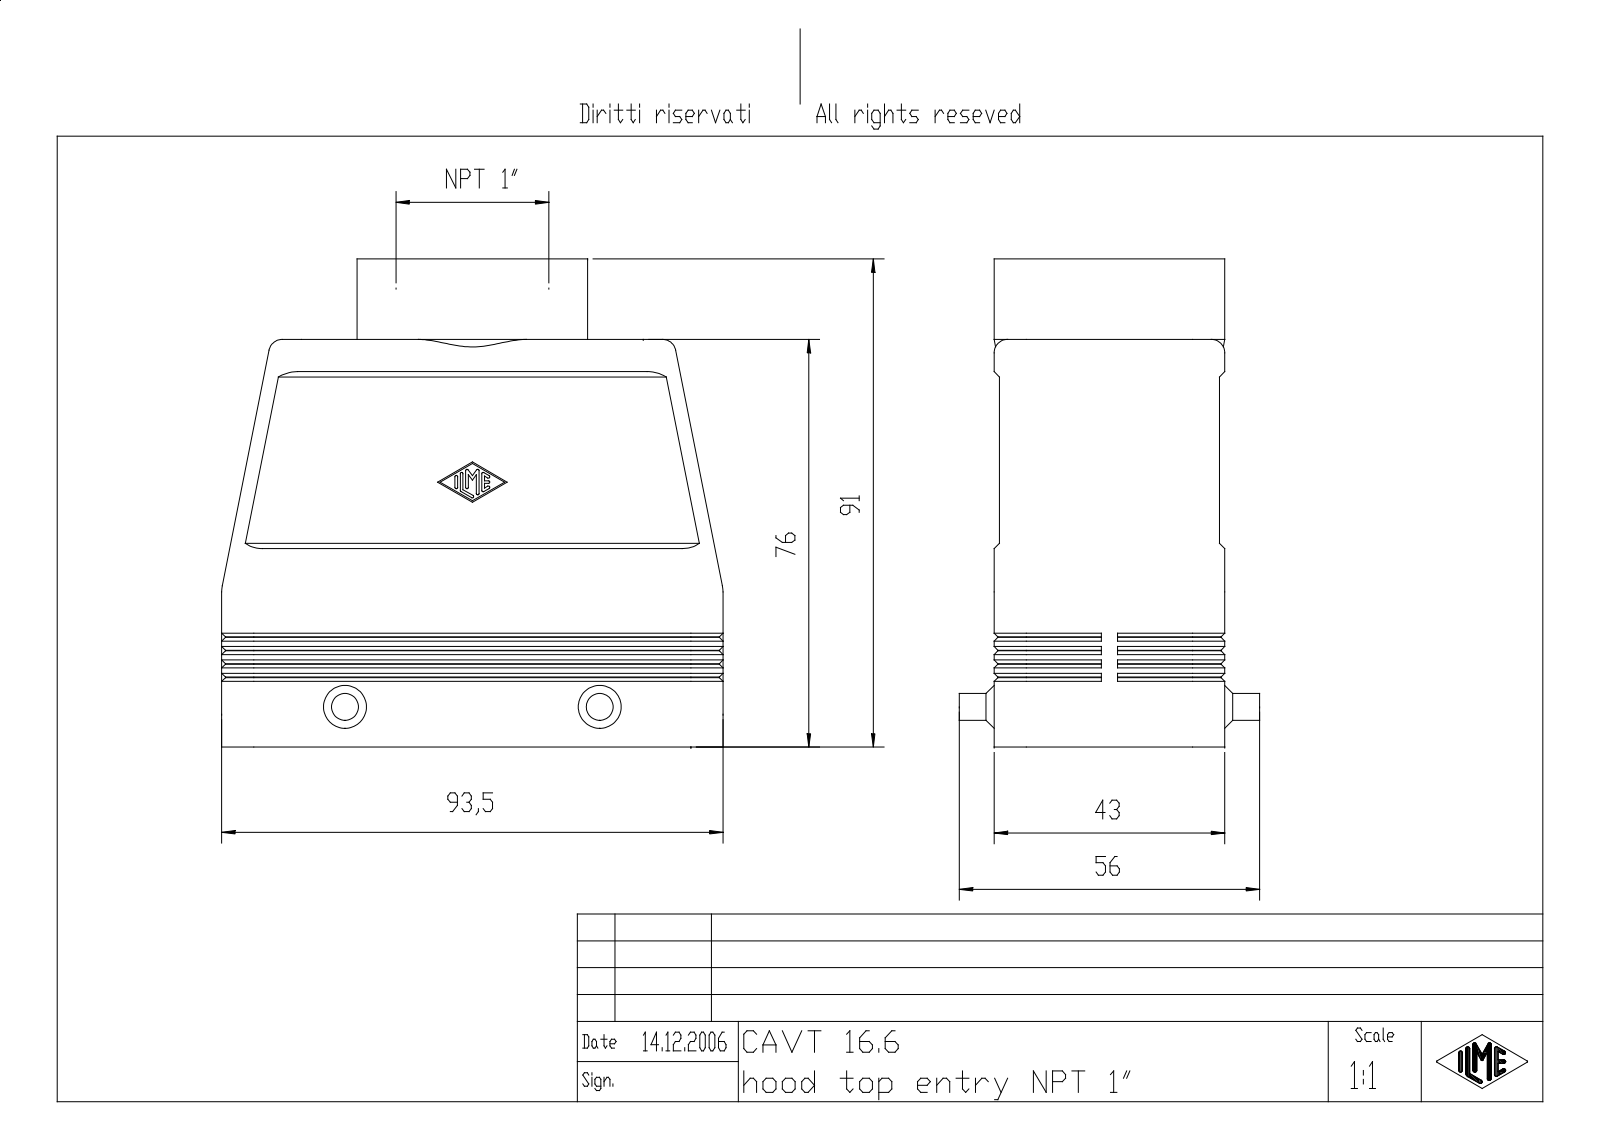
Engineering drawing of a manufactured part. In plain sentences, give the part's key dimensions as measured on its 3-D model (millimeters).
The part is named "MSBO6839". Its 3-D file was written by "Creo Elements/Direct Modeling 18.0B 02-Dec-2011 (C) Parametric Technology GmbH (AUTOMOTIVE_DESIGN)". It is 1 solid with 334 faces: 178 planar, 97 cylindrical and 59 other. Overall it measures 93.5 by 91 by 56 millimeters. Its volume is 82 427 cubic millimeters and its surface area 46 560 square millimeters. Round holes: 4 of diameter 4, 3 of diameter 2.46, 1 of diameter 2.46. Round bosses or shafts: 2 of diameter 5, 1 of diameter 43. Partial cylindrical surfaces (rounded edges, fillets, slot ends): 14 of radius 0.25, 10 of radius 6, 4 of radius 2, 4 of radius 2.5, 4 of radius 3, 4 of radius 5.3. The main face-to-face distances are 3, 40, 37, 2, 1, 42, 39, 43, 41, 12.25. The hole center spacings are 27, 77.5, 82.07.
